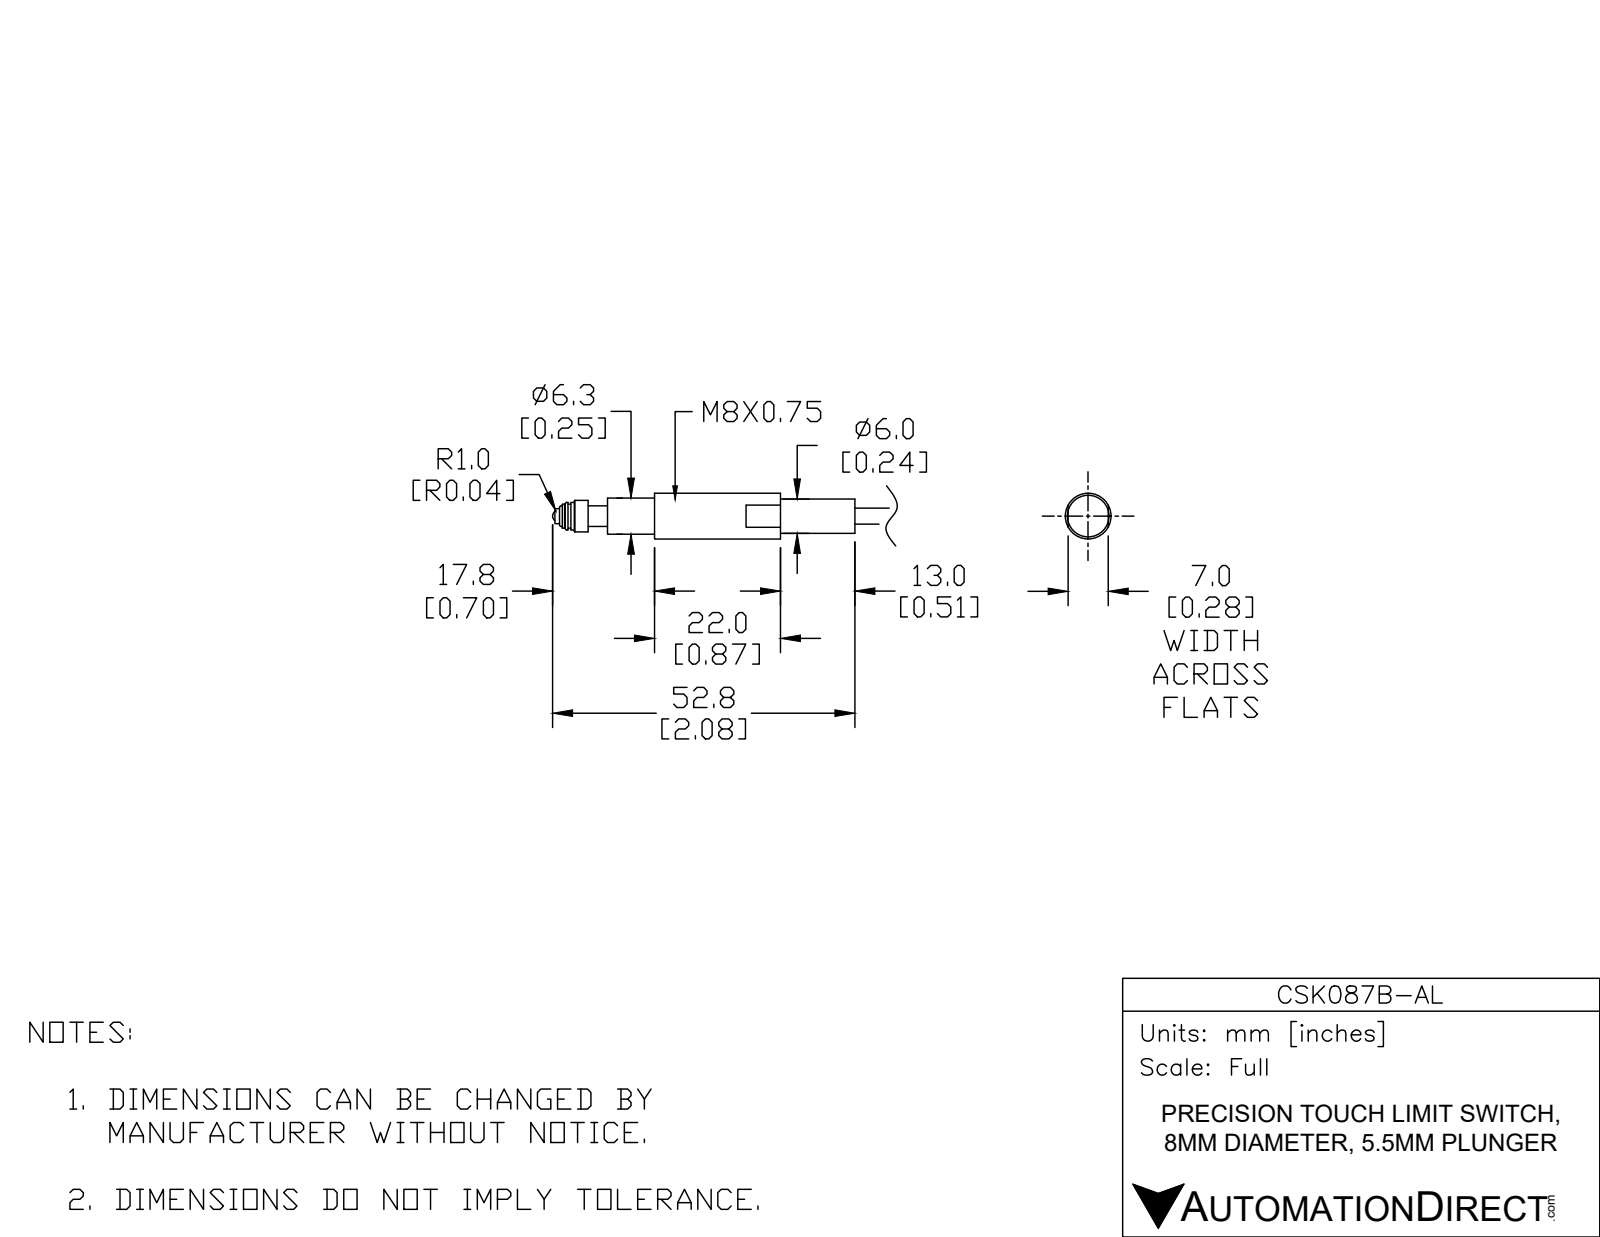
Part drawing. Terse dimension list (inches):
name: CSP087B-A
written by: SolidWorks 2017 (AUTOMOTIVE_DESIGN)
unit: in
bodies: 1 solid, 159 faces (18 planar, 83 cylindrical, 58 other)
size: 2.315 × 0.315 × 0.315
volume: 0.108 in³; area: 2.418 in²
bosses: 1× ⌀0.315, 1× ⌀0.248, 1× ⌀0.236, 1× ⌀0.217, 1× ⌀0.189, 1× ⌀0.165, 1× ⌀0.142, 1× ⌀0.11
face distances: 1.701, 0.134, 0.276, 0.02, 1.189, 0.512, 1.323, 1.835, 0.457, 0.323
